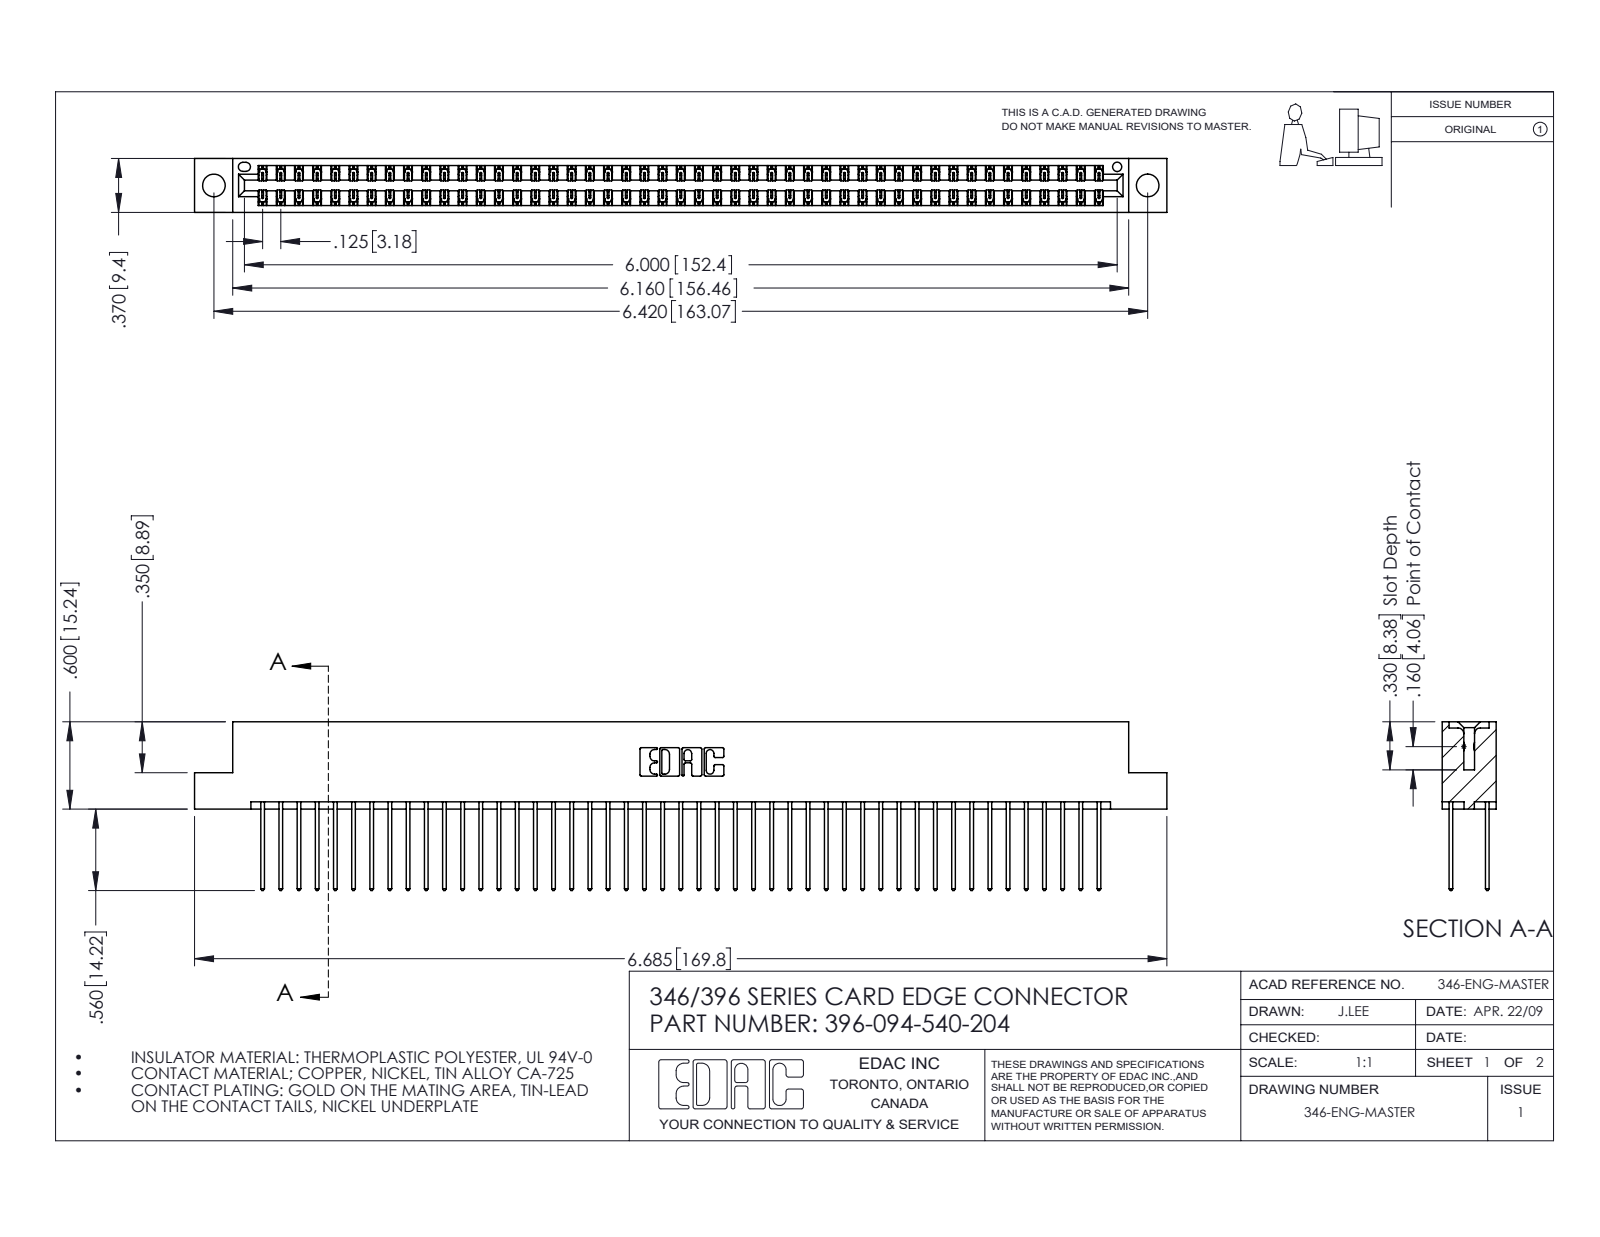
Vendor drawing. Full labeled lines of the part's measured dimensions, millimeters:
Part name (STEP PRODUCT): 345-292-001_345-293-140; 396-094-540-204; 346 Part_Flush Mounting Lugs - 0.156 Dia-TH
STEP written by: SolidWorks 2016 (CONFIG_CONTROL_DESIGN)
Units: millimetres
Bodies: 95 solids, 5010 faces (3366 planar, 1644 cylindrical, 0 other)
Overall size (bounding box): 169.8 × 29.5 × 9.4
Volume: 16 860 mm³ · Surface area: 24 760 mm²
Round holes (diameter × count): ⌀4 ×2, ⌀1.6 ×1
Partial cylindrical surfaces — rounded edges, fillets, slot ends (radius × count): R0.2 ×141, R0.3 ×94, R0.3 ×22, R0.2 ×6, R0.8 ×6, R0.7 ×3, R0.4 ×2, R0.6 ×2
Main face-to-face distances: 1.2, 8.2, 6.4, 1.8, 7.6, 0.6, 9.4, 7, 3.8, 5.6
Hole centre spacings: 6.2, 157.8, 163.1
